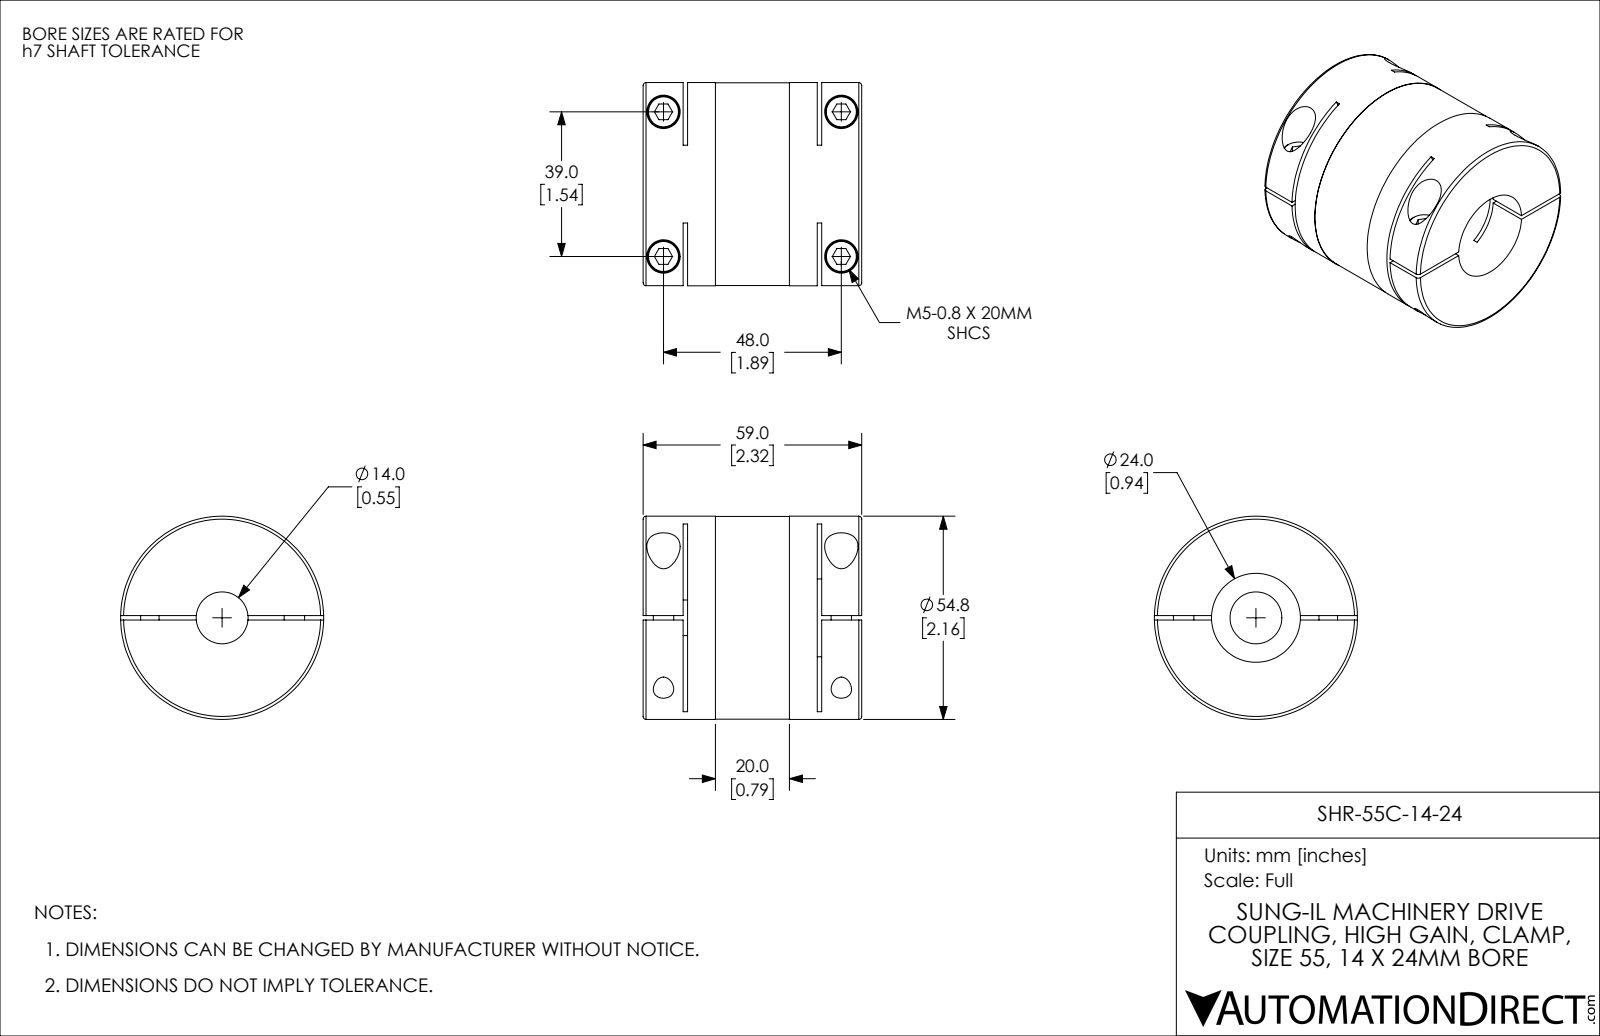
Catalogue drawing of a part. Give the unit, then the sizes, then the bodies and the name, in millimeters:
Units: millimetres
Overall size (bounding box): 59 × 54.8 × 54.8
Round holes (diameter × count): ⌀5.5 ×4, ⌀9 ×4, ⌀14 ×1, ⌀24 ×1, ⌀26 ×1
Round bosses / shafts (diameter × count): ⌀8.5 ×4, ⌀5 ×2, ⌀54.8 ×1, ⌀54.7 ×1
Partial cylindrical surfaces — rounded edges, fillets, slot ends (radius × count): R60 ×2
Main face-to-face distances: 1.2, 12, 47, 10.8, 48.2, 36.2, 59, 35, 37.4, 19.5
Hole centre spacings: 39, 48, 61.85
Volume: 109 263 mm³ · Surface area: 29 004 mm²
Bodies: 1 solid, 144 faces (70 planar, 58 cylindrical, 16 other)
Part name (STEP PRODUCT): SHR-55C-14-24
STEP written by: SolidWorks 2021 (CONFIG_CONTROL_DESIGN)
